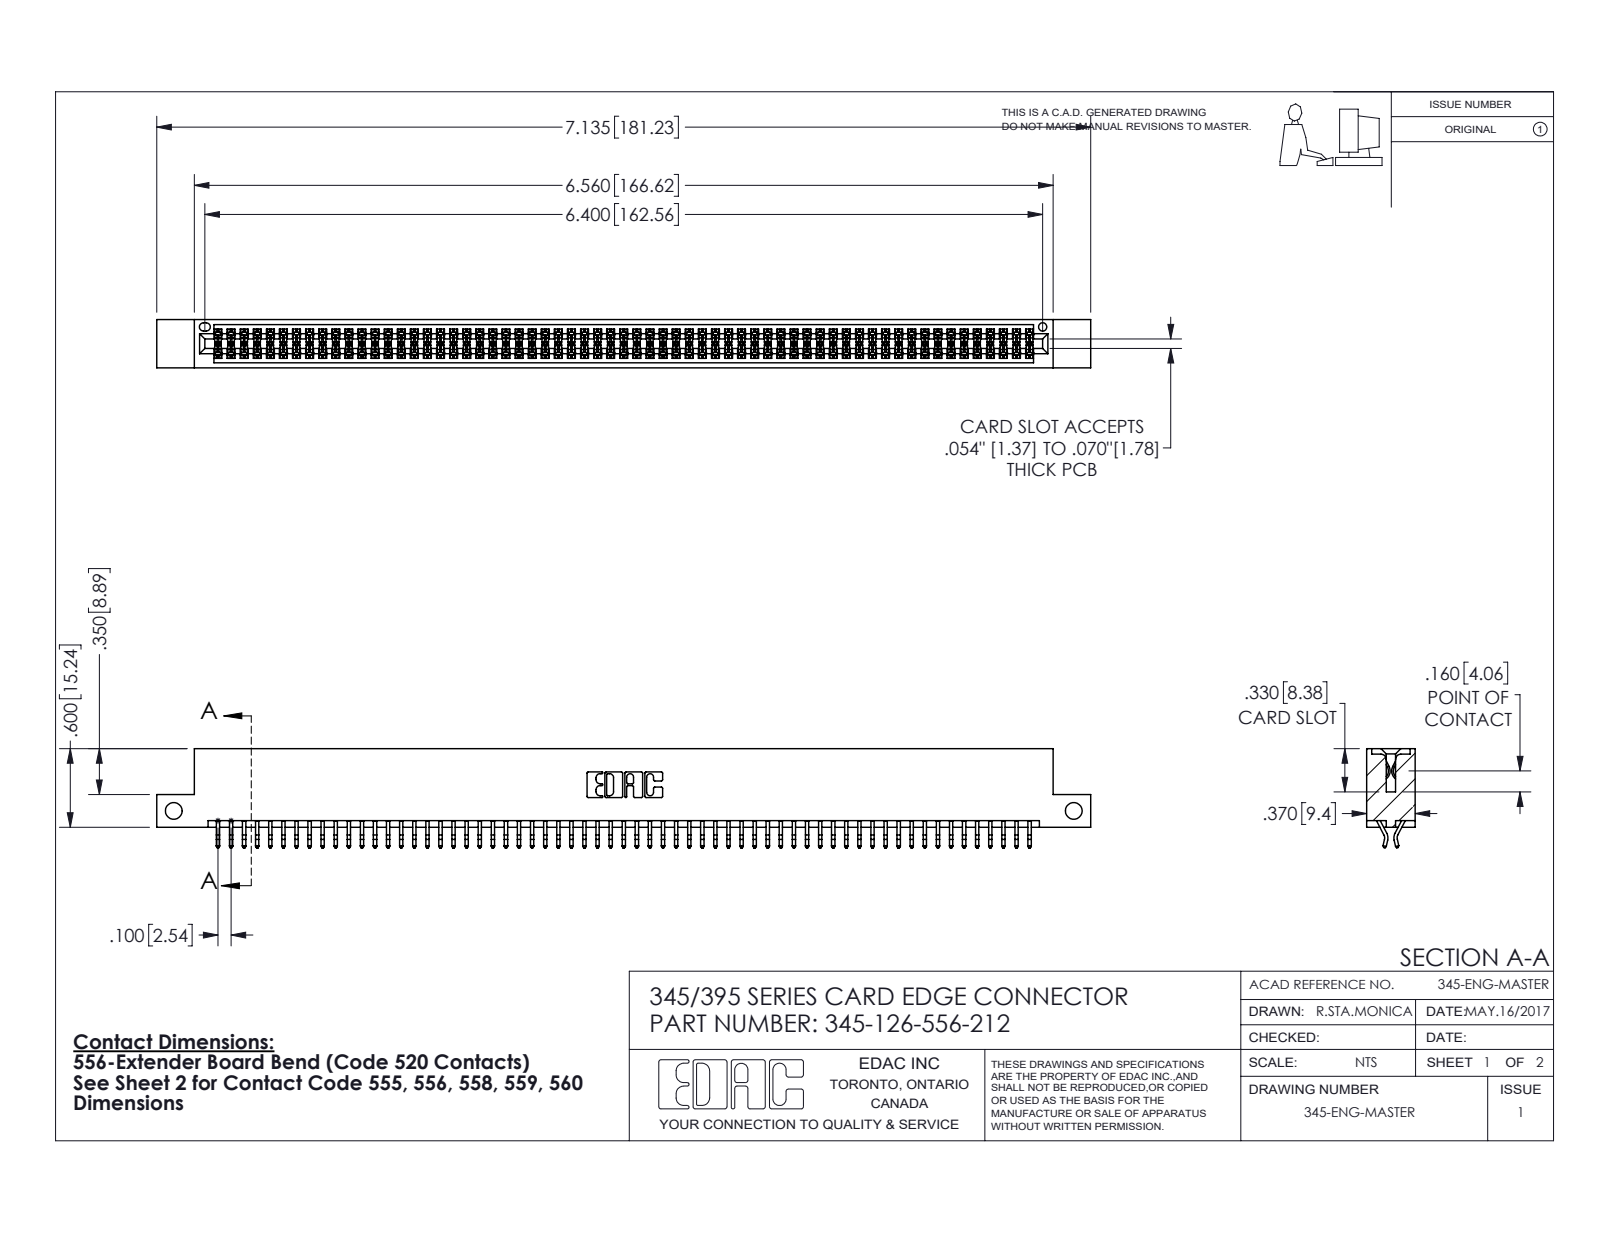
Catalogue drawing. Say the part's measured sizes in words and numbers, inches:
The part is named "345-292-001_556 Tail; 345-126-556-212; 345 Part_Flush Mounting Lugs - Side Mount". Its 3-D file was written by "SolidWorks 2016 (CONFIG_CONTROL_DESIGN)". It is 127 solids with 7182 faces: 4742 planar, 2440 cylindrical and 0 other. Overall it measures 7.135 by 0.757 by 0.37 inches. Its volume is 1.081 cubic inches and its surface area 40.82 square inches. Round holes: 2 of diameter 0.128, 1 of diameter 0.064. Partial cylindrical surfaces (rounded edges, fillets, slot ends): 189 of radius 0.006, 22 of radius 0.01, 6 of radius 0.007, 6 of radius 0.031, 3 of radius 0.026, 2 of radius 0.01, 2 of radius 0.014, 2 of radius 0.019. The main face-to-face distances are 0.298, 0.072, 0.2, 0.37, 0.025, 0.098, 0.272, 0.225, 0.175, 0.149. The hole center spacings are 6.875.
